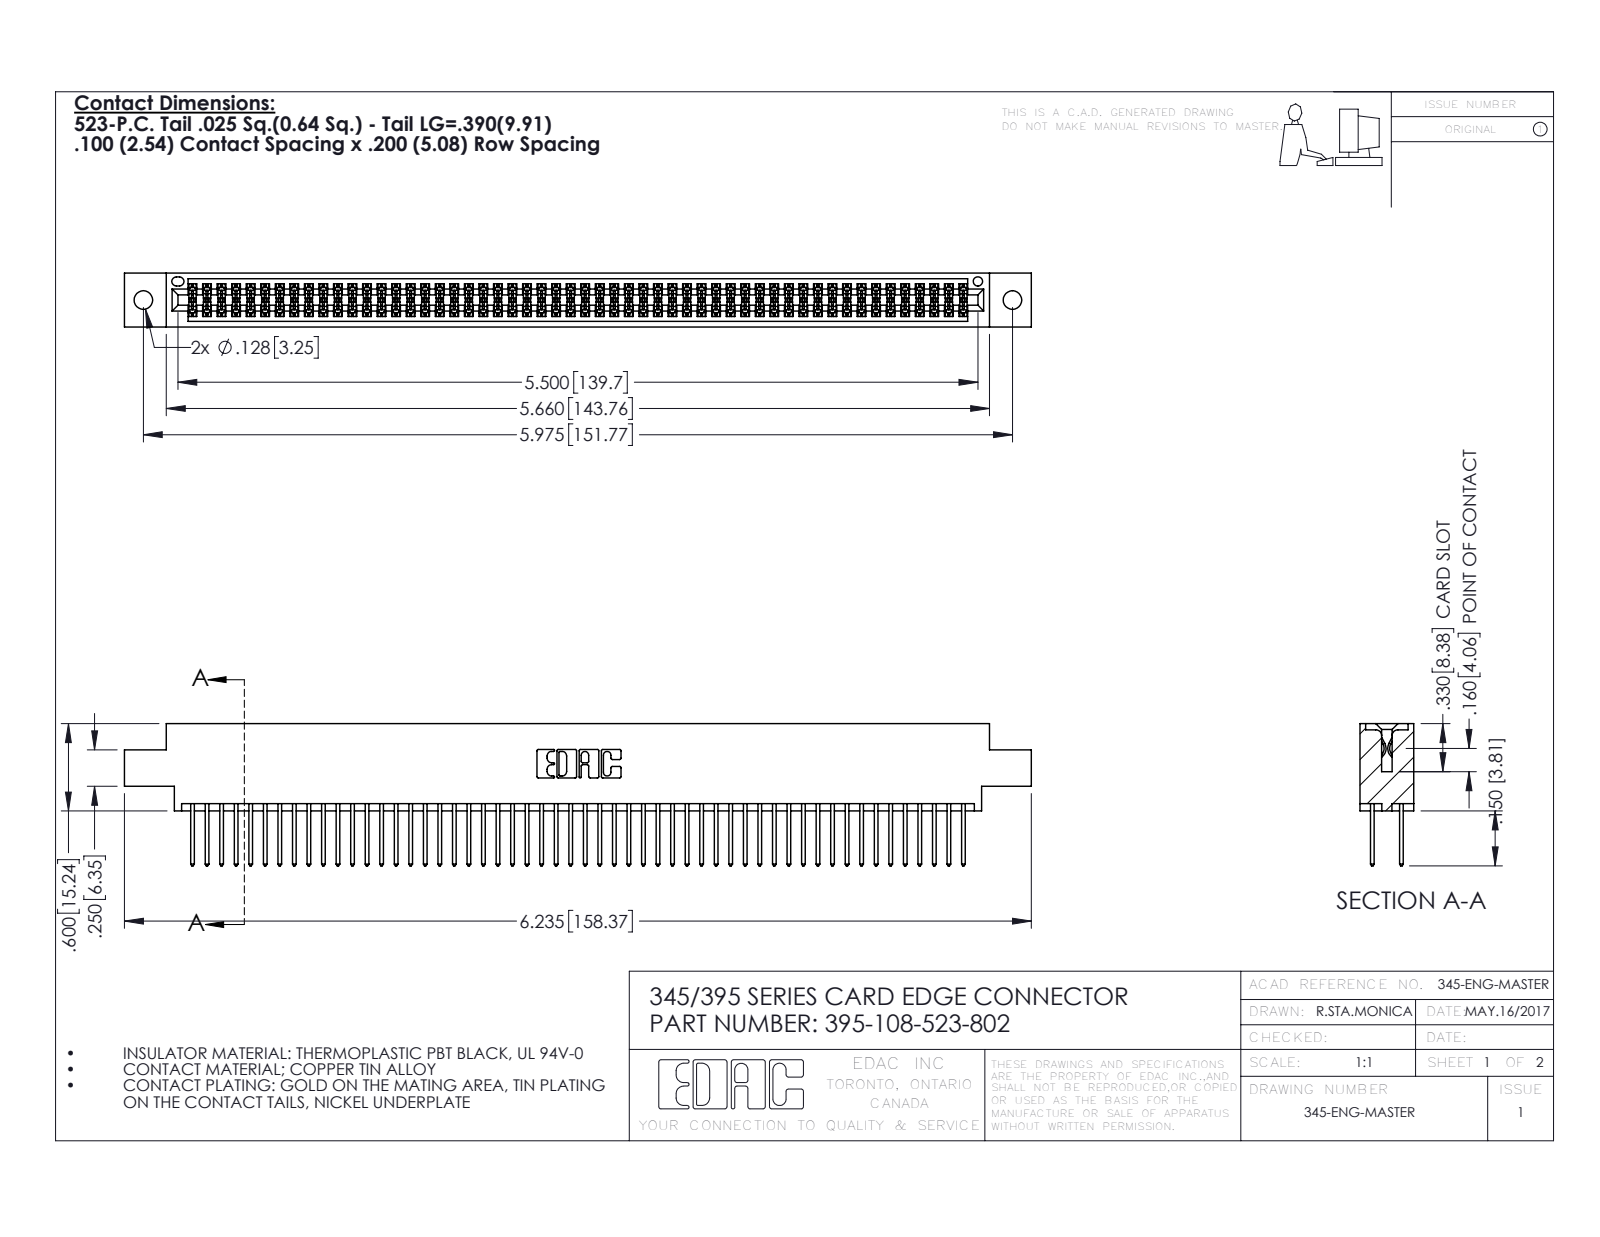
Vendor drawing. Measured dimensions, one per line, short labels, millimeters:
name: 345 Part_0.170 Offset - 0.128 Dia; 345-292-001_345-293-123; 395-108-523-802
written by: SolidWorks 2016 (CONFIG_CONTROL_DESIGN)
unit: mm
bodies: 109 solids, 5530 faces (3648 planar, 1882 cylindrical, 0 other)
size: 158.4 × 24.8 × 9.4
volume: 15 600 mm³; area: 24 110 mm²
holes: 2× ⌀3.3, 1× ⌀1.6
rounds: 162× R0.2, 108× R0.3, 22× R0.3, 6× R0.2, 6× R0.8, 3× R0.7, 2× R0.4, 2× R0.5
face distances: 7.6, 1.8, 5.1, 2.5, 6.9, 0.6, 9.4, 5.7, 4.4, 3.8
hole spacings: 6.9, 145.8, 151.8
